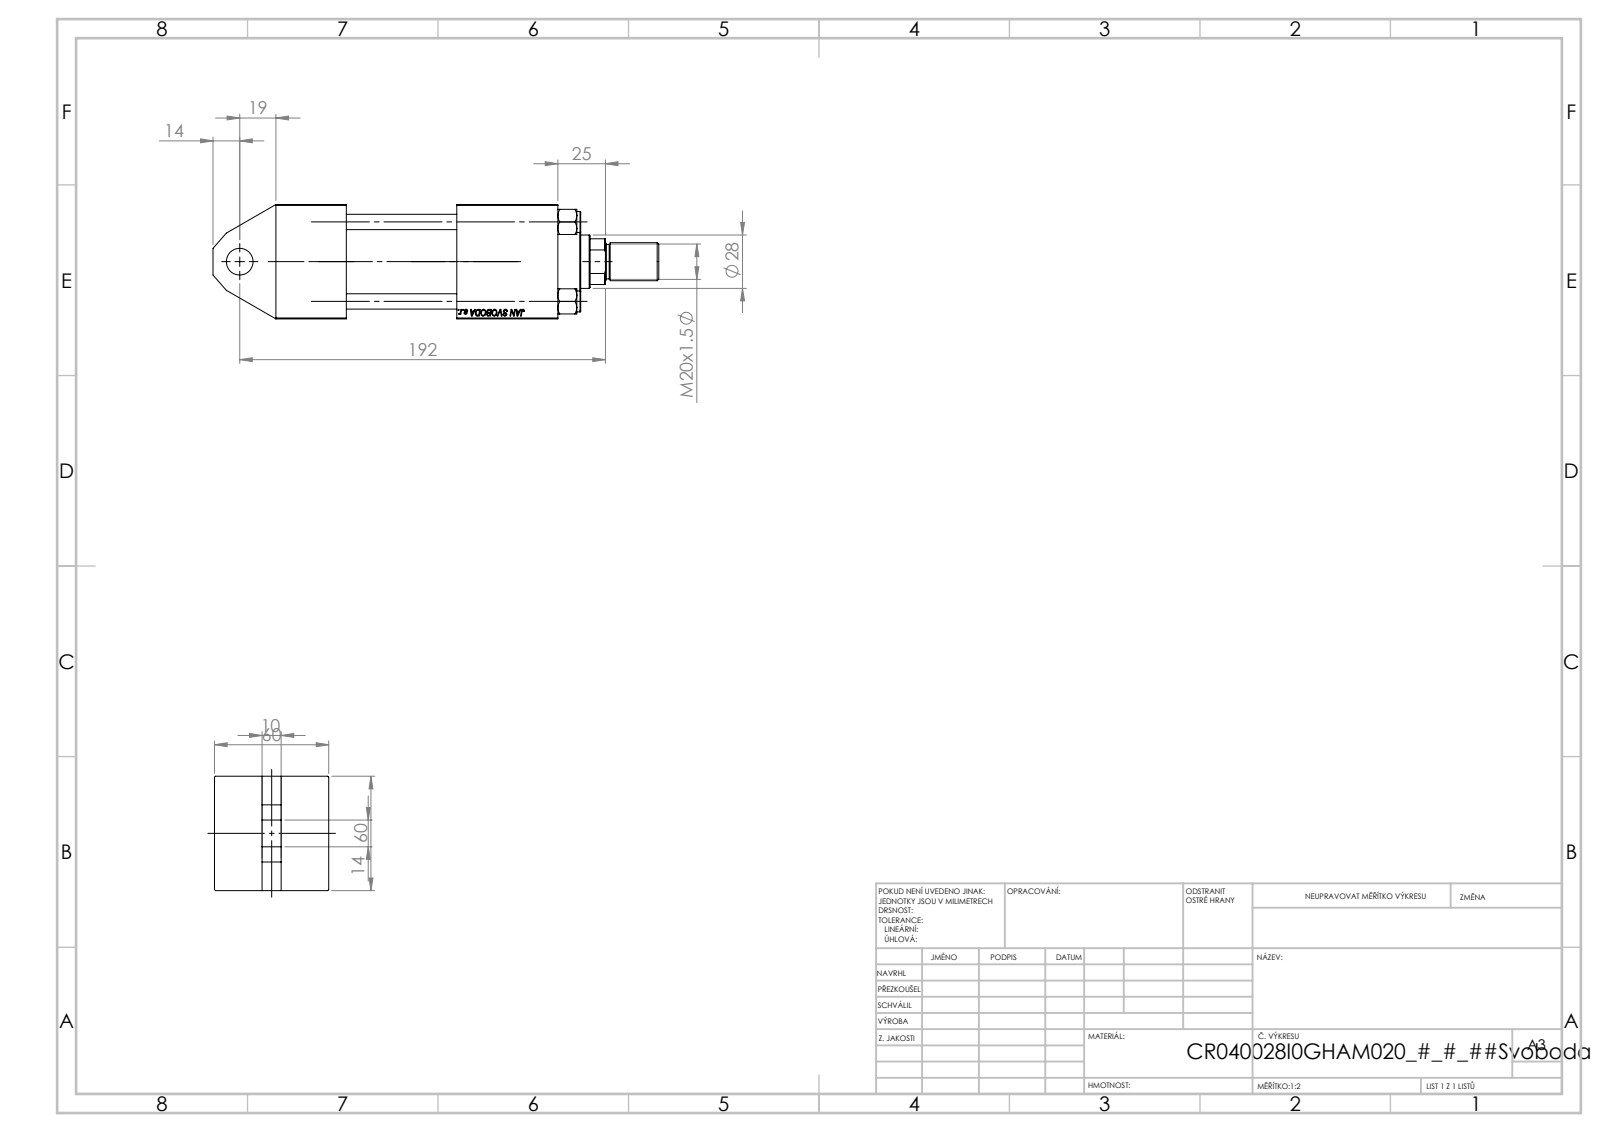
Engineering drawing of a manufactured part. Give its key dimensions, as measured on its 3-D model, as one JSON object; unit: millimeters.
{"part_name": "V215CR_VCP_I; V215CR_TYCINKA_I; NUT_M5_I; V215CR_I_Body (+2 more)", "step_written_by": "SolidWorks 2019 (CONFIG_CONTROL_DESIGN)", "units": "millimeters", "bodies": {"solids": 12, "faces": 1093, "planar": 506, "cylindrical": 85, "other": 502}, "overall_size": [234, 60, 60], "volume_mm3": 448508, "surface_area_mm2": 118116, "round_holes": [[8, 4], [7, 2], [16.66, 2], [24, 2], [14, 1], [18.5, 1], [28, 1], [31, 1], [40, 1], [45, 1]], "round_bosses_or_shafts": [[11, 4], [46, 1], [42, 1], [20, 1], [18, 1]], "partial_cylinders_radius": [[13.5, 1]], "face_to_face_distances": [60, 37, 25, 53, 35, 58, 95, 148, 111, 119.3], "hole_center_spacings": [29.49, 41.7, 58.97, 37.5, 92.5, 130]}
